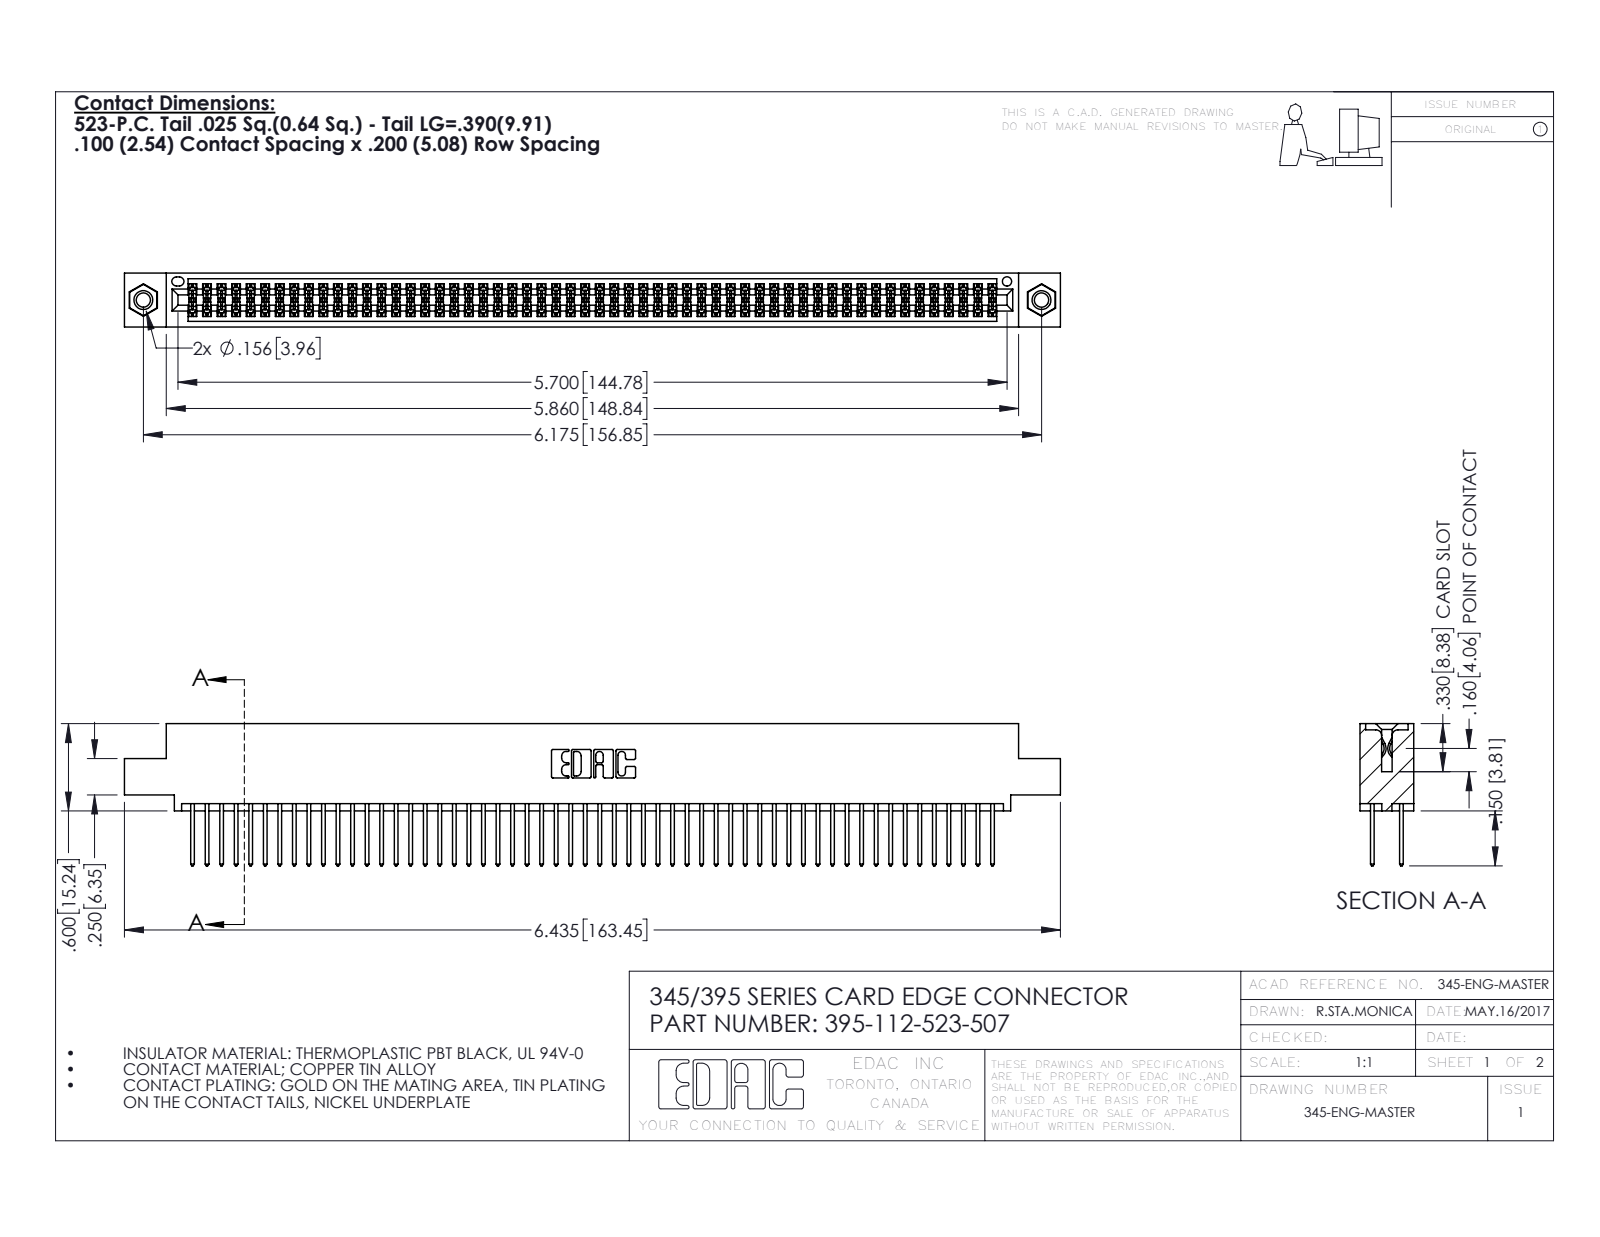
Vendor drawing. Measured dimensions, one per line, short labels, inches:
name: 345-292-001_345-293-123; 345-250-001_345-250-005-103; 345 Part_0.110 Offset - 0.156 Dia-TI; 395-112-523-507
written by: SolidWorks 2016 (CONFIG_CONTROL_DESIGN)
unit: in
bodies: 115 solids, 5790 faces (3812 planar, 1962 cylindrical, 16 other)
size: 6.435 × 0.977 × 0.37
volume: 0.986 in³; area: 39.21 in²
holes: 2× ⌀0.098, 2× ⌀0.125, 2× ⌀0.156, 1× ⌀0.064
bosses: 2× ⌀0.155
rounds: 168× R0.006, 112× R0.01, 22× R0.01, 6× R0.007, 6× R0.031, 3× R0.026, 2× R0.014, 2× R0.019
face distances: 0.072, 0.298, 0.2, 0.098, 0.272, 0.025, 0.37, 0.225, 0.175, 0.149
hole spacings: 0.27, 5.939, 6.175
